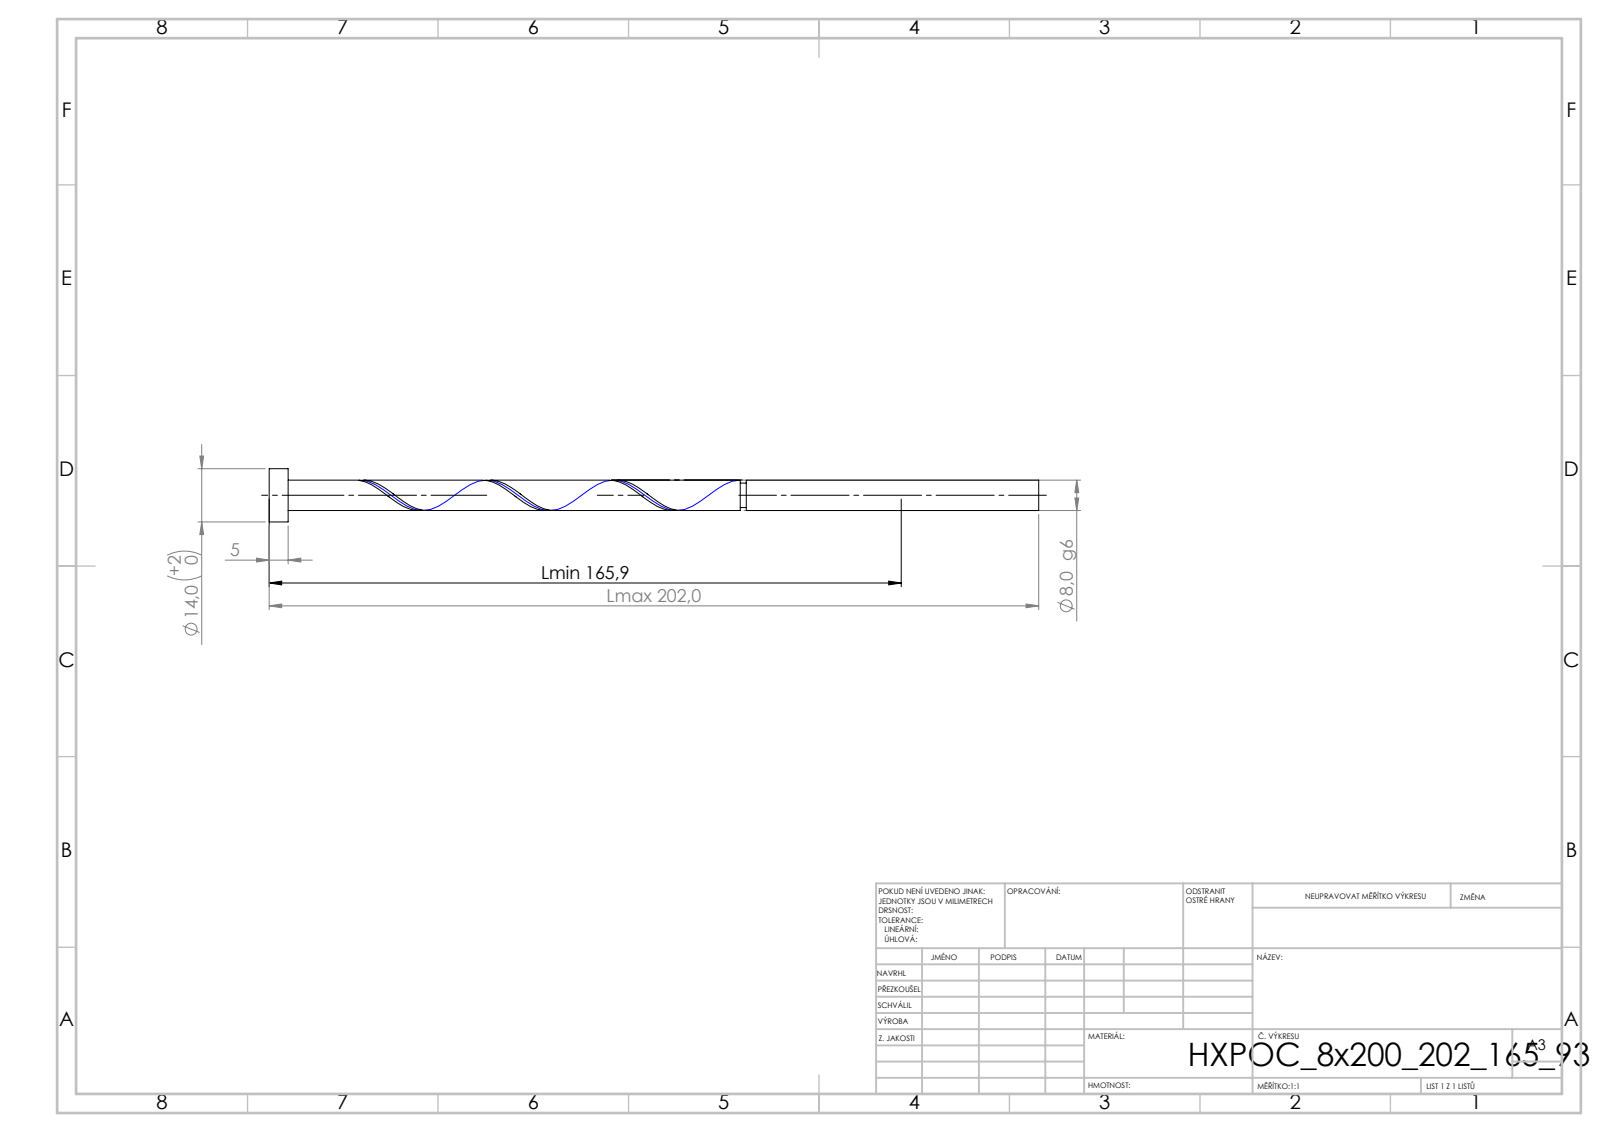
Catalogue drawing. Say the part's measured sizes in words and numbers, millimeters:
Its 3-D file was written by "SolidWorks 2019 (CONFIG_CONTROL_DESIGN)". It is 1 solid with 21 faces: 6 planar, 14 cylindrical and 1 other. Overall it measures 202 by 14 by 14 millimeters. Its volume is 10 547 cubic millimeters and its surface area 5 611 square millimeters. Round bosses or shafts: 1 of diameter 14, 1 of diameter 8, 1 of diameter 6.4. The main face-to-face distances are 5, 202, 197, 125.26, 120.26, 76.74, 123.66, 118.66, 1.6, 78.34.
